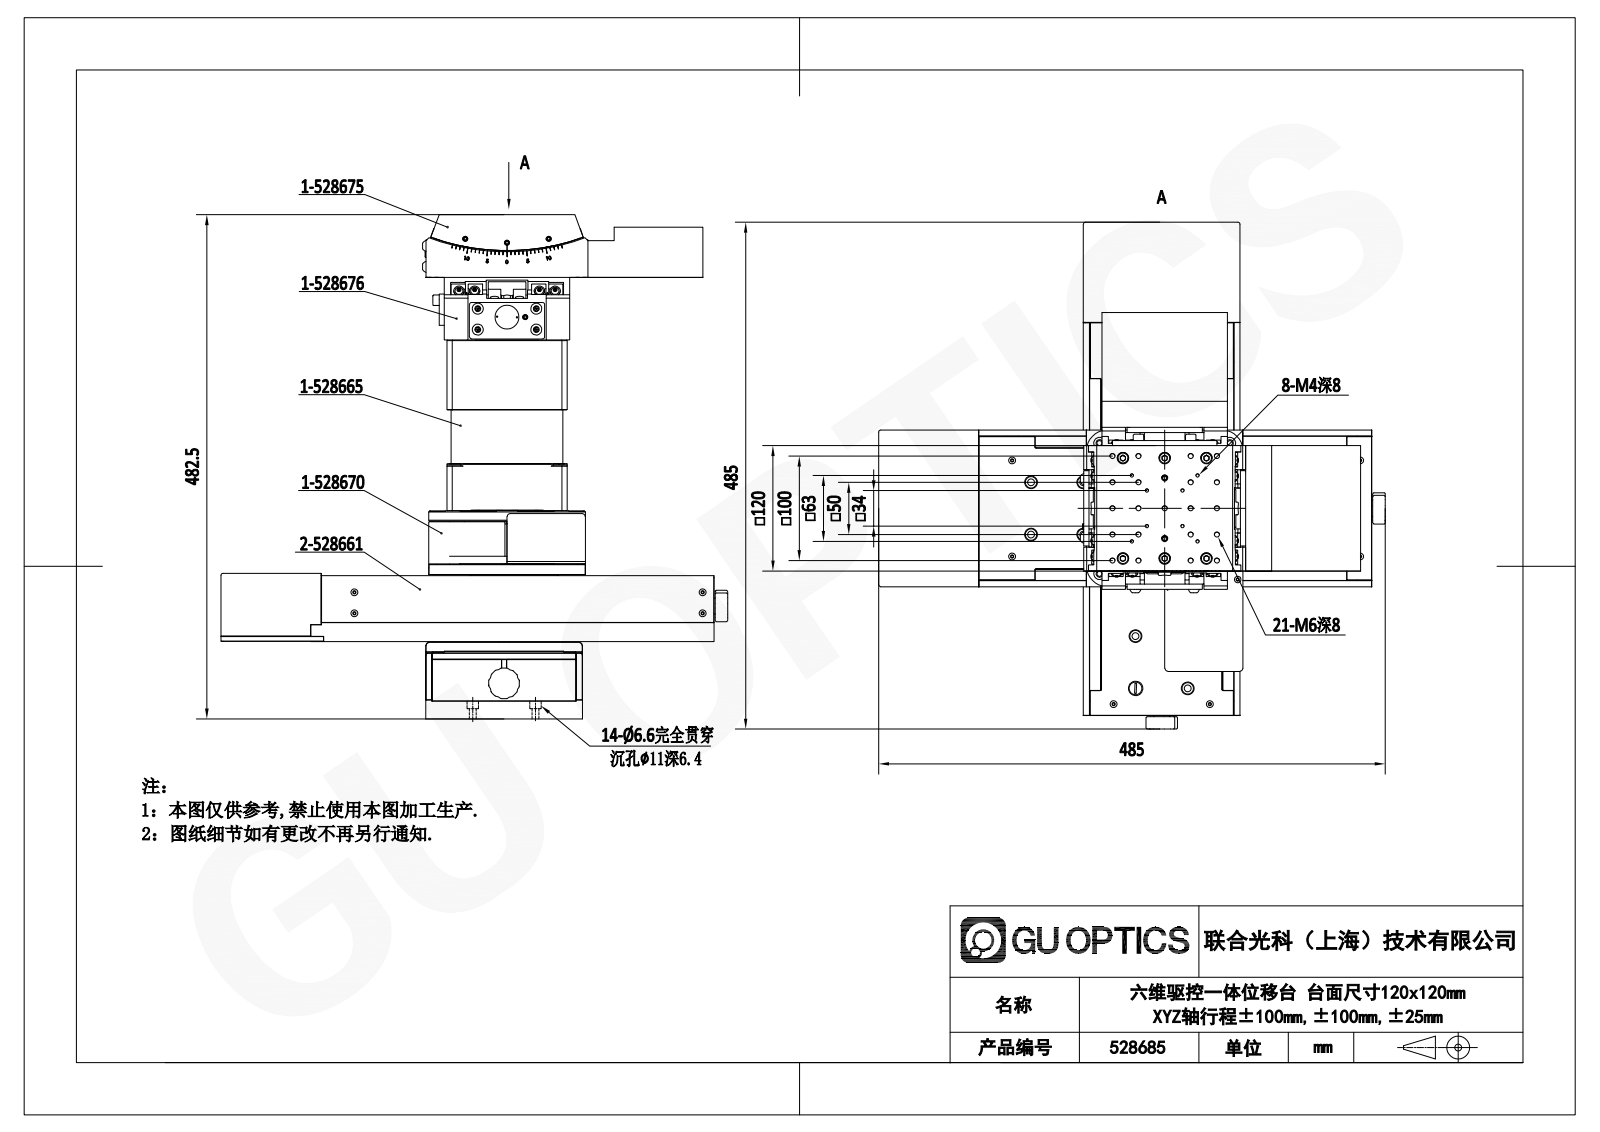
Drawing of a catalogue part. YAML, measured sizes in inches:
part_name: "528685; 528665; 528676; 528675 (+2 more)"
step_written_by: "SolidWorks 2020 (CONFIG_CONTROL_DESIGN)"
units: inches
bodies: {solids: 263, faces: 10568, planar: 6553, cylindrical: 2280, other: 1735}
overall_size: [19.094, 19.094, 18.996]
volume: 560.9
surface_area: 4044
round_holes:
  - {diameter: 0.197, count: 175}
  - {diameter: 0.13, count: 107}
  - {diameter: 0.134, count: 82}
  - {diameter: 0.098, count: 80}
  - {diameter: 0.256, count: 73}
  - {diameter: 0.433, count: 67}
  - {diameter: 0.26, count: 51}
  - {diameter: 0.315, count: 48}
  - {diameter: 0.138, count: 32}
  - {diameter: 0.236, count: 29}
  - {diameter: 0.492, count: 28}
  - {diameter: 0.097, count: 24}
round_bosses_or_shafts:
  - {diameter: 0.157, count: 44}
  - {diameter: 0.236, count: 35}
  - {diameter: 0.394, count: 32}
  - {diameter: 0.276, count: 24}
  - {diameter: 0.374, count: 8}
  - {diameter: 0.335, count: 8}
  - {diameter: 0.098, count: 8}
  - {diameter: 0.197, count: 7}
partial_cylinders:
  - {radius: 0.197, count: 93}
  - {radius: 0.079, count: 59}
  - {radius: 0.039, count: 45}
  - {radius: 0.012, count: 36}
  - {radius: 0.138, count: 20}
  - {radius: 0.118, count: 19}
  - {radius: 0.295, count: 18}
  - {radius: 0.157, count: 10}
face_to_face_distances: [2.913, 0.236, 2.244, 2.48, 0.669, 1.772, 0.709, 1.535, 0.098, 0.413]
hole_center_spacings: [0.492, 2.461, 0.984, 1.476, 1.969, 1.1, 1.556, 2.029]
